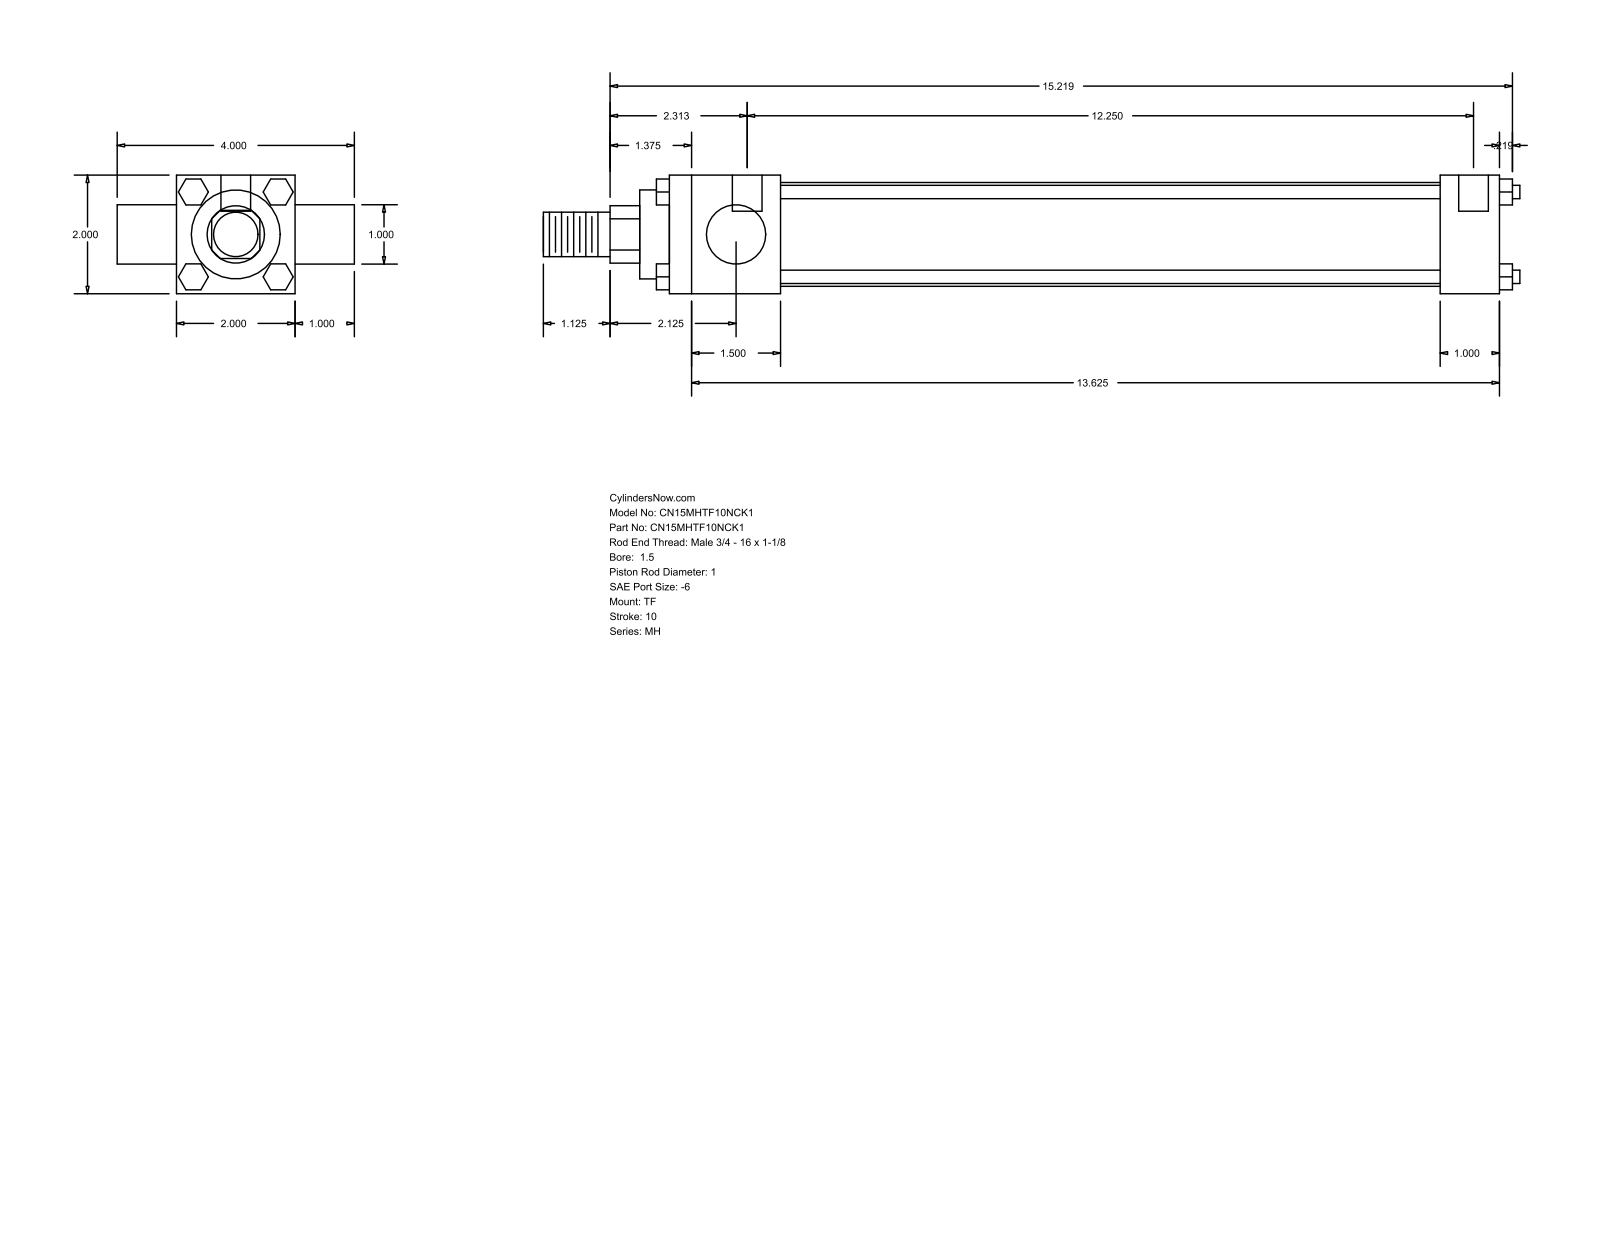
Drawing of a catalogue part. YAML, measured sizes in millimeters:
part_name: "MH_TF__0150_1"
step_written_by: "GSSL Pune (CONFIG_CONTROL_DESIGN)"
units: millimeters
bodies: {solids: 0, faces: 120, planar: 92, cylindrical: 28, other: 0}
overall_size: [418.31, 101.6, 50.8]
round_holes:
  - {diameter: 5.56, count: 3}
  - {diameter: 12.7, count: 2}
round_bosses_or_shafts:
  - {diameter: 5.71, count: 4}
  - {diameter: 25.4, count: 2}
  - {diameter: 44.45, count: 1}
  - {diameter: 38.1, count: 1}
  - {diameter: 19.05, count: 1}
partial_cylinders:
  - {radius: 12.29, count: 1}
face_to_face_distances: [50.8, 25.4, 355.6, 76.2, 47.63, 307.97, 330.2, 282.57, 101.6, 12.7]
hole_center_spacings: [3.18, 311.15, 314.33]
